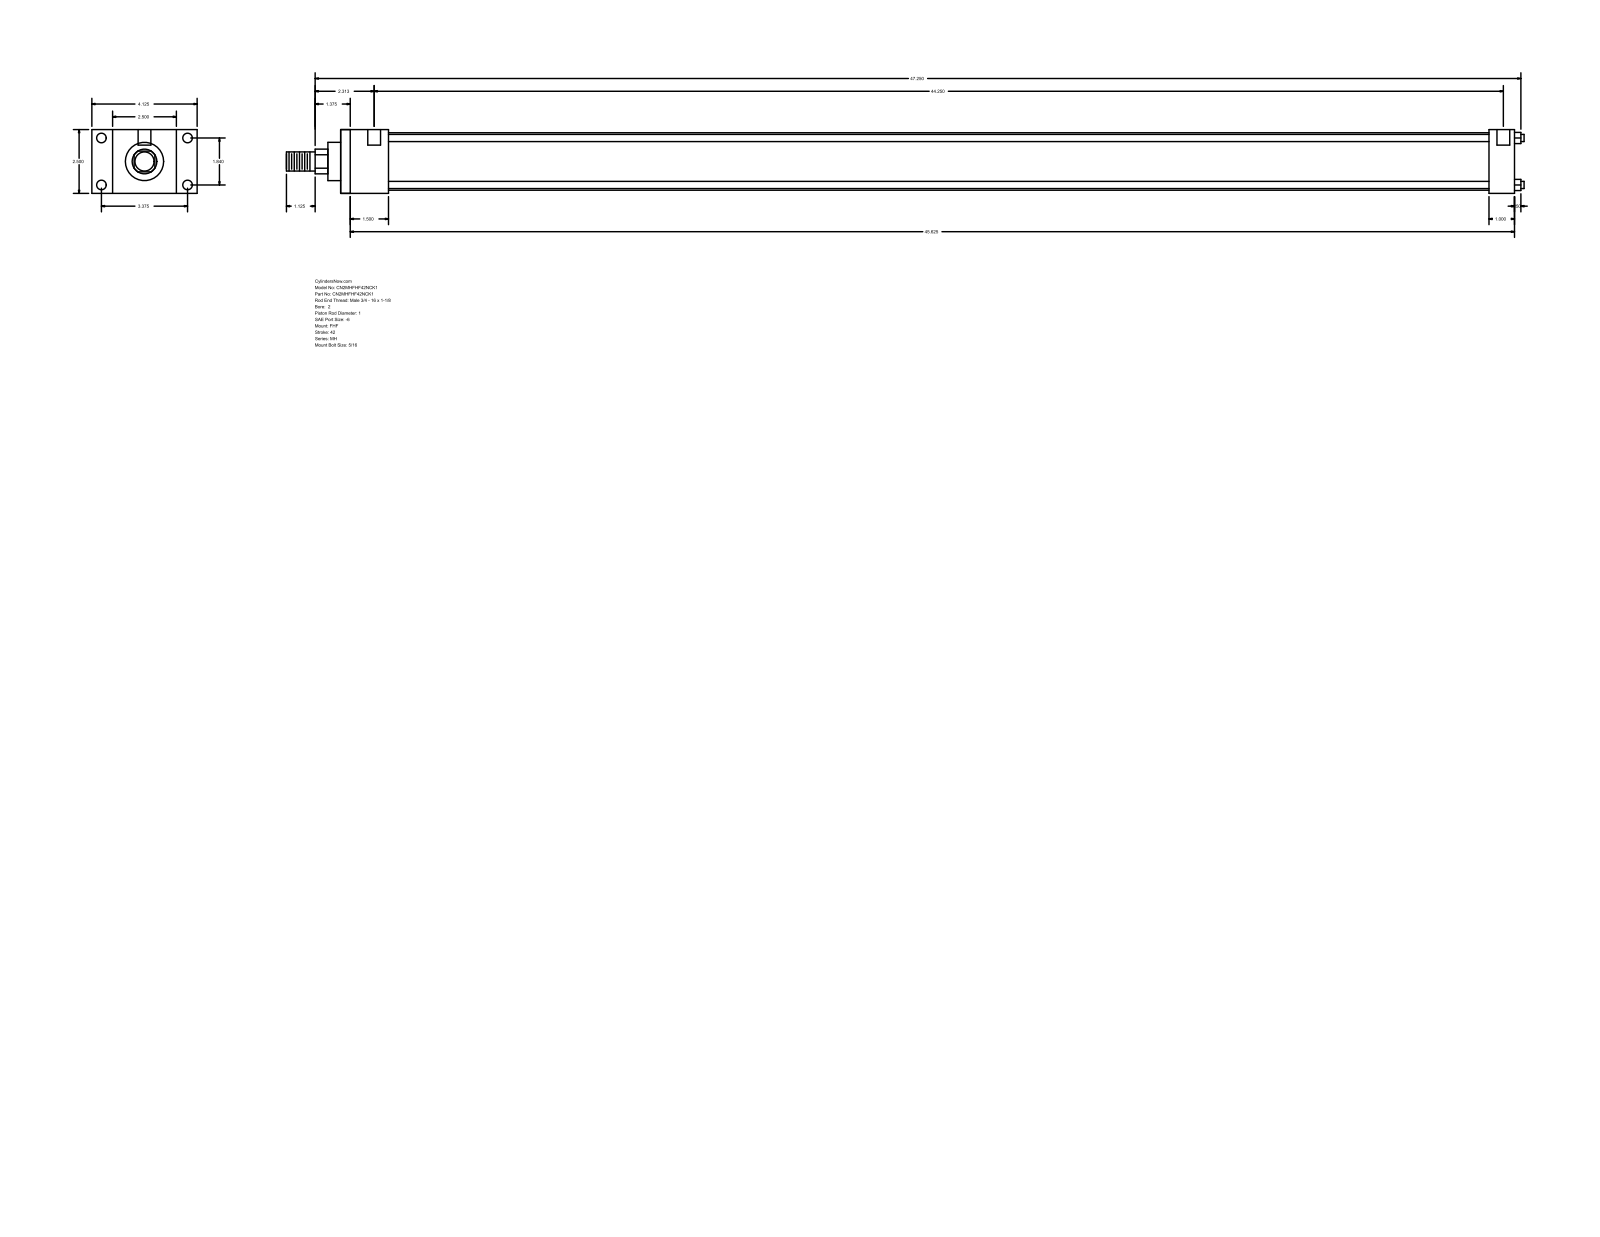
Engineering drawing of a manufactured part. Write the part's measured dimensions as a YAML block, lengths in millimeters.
part_name: "MH_FHF__0200_1"
step_written_by: "GSSL Pune (CONFIG_CONTROL_DESIGN)"
units: millimeters
bodies: {solids: 0, faces: 88, planar: 60, cylindrical: 28, other: 0}
overall_size: [1231.9, 104.78, 63.5]
round_holes:
  - {diameter: 5.56, count: 4}
  - {diameter: 9.53, count: 4}
  - {diameter: 12.7, count: 2}
round_bosses_or_shafts:
  - {diameter: 7.14, count: 4}
  - {diameter: 57.15, count: 1}
  - {diameter: 38.1, count: 1}
  - {diameter: 25.4, count: 1}
  - {diameter: 19.05, count: 1}
partial_cylinders:
  - {radius: 12.29, count: 1}
face_to_face_distances: [63.5, 1168.4, 47.63, 1120.77, 20.64, 84.14, 104.78, 25.4, 1143, 1095.37]
hole_center_spacings: [46.74, 85.72, 97.63, 1131.88, 3.17, 4.76, 1123.95, 1127.12]
